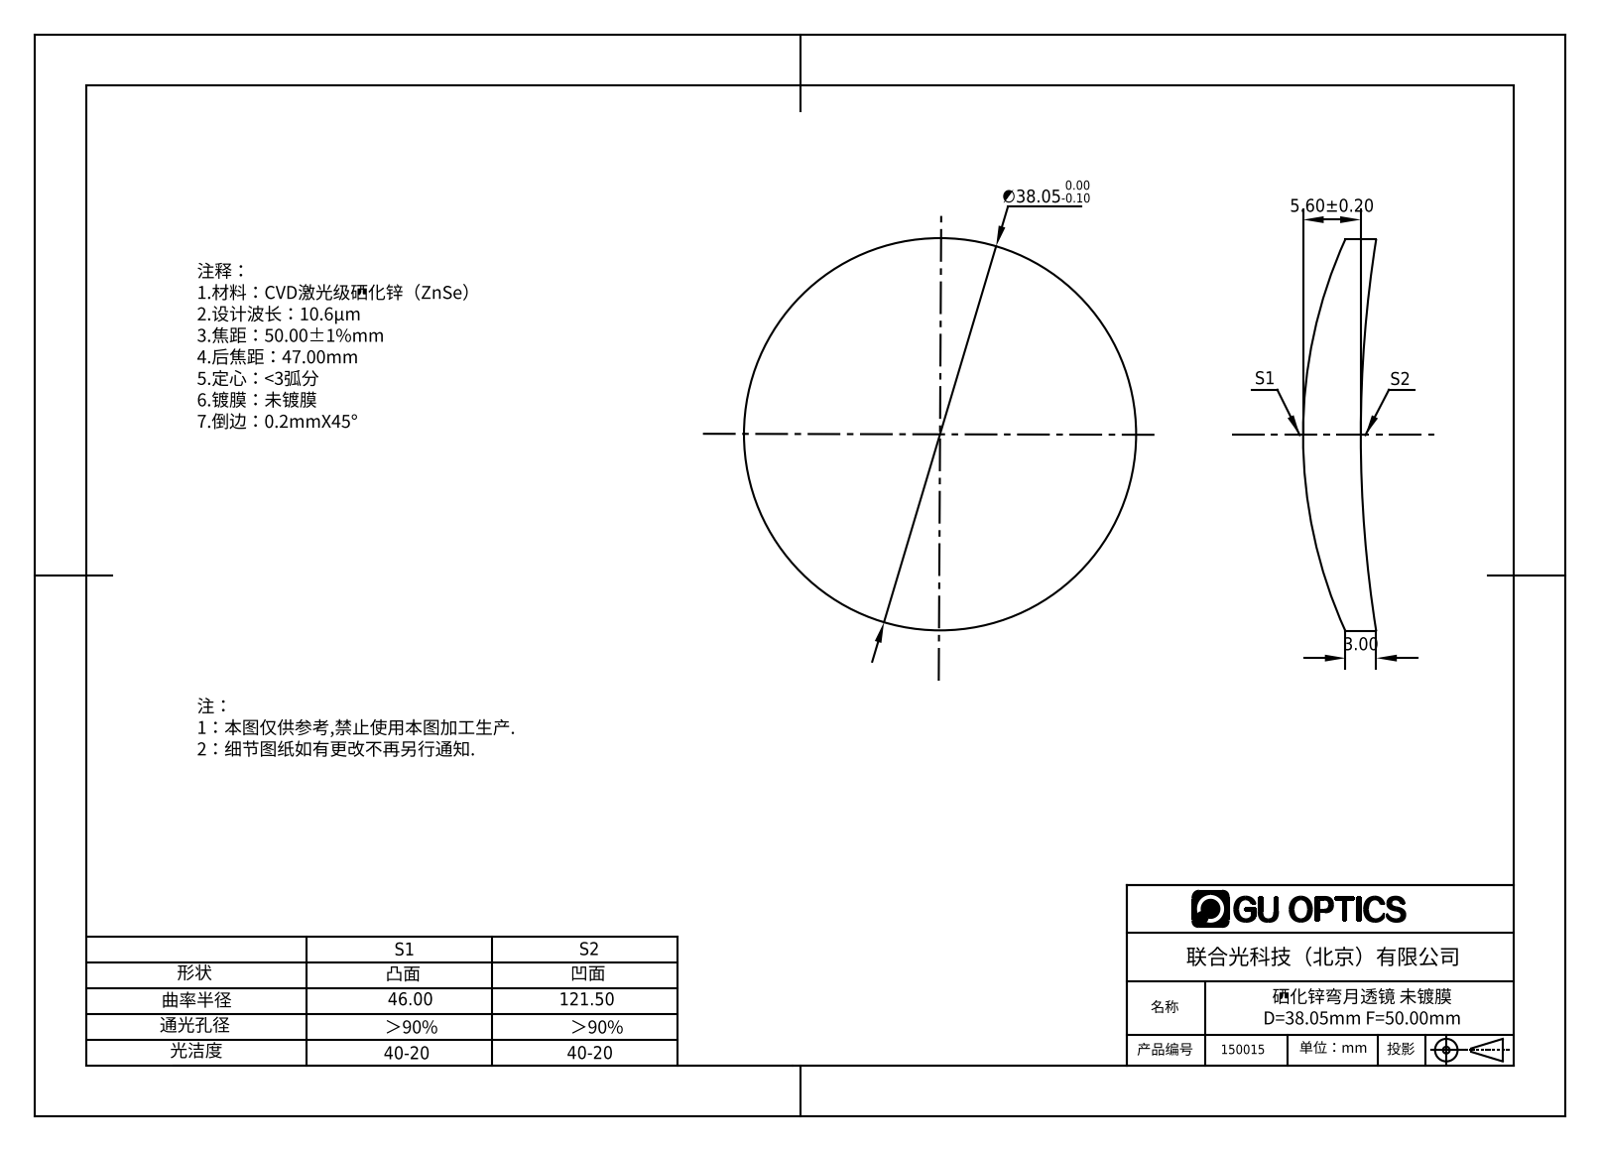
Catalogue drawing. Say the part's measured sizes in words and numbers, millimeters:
The part is named "150015". Its 3-D file was written by "SolidWorks 2016 (AUTOMOTIVE_DESIGN)". It is 1 solid with 6 faces: 0 planar, 2 cylindrical and 4 other. Overall it measures 38.05 by 38.05 by 7.1 millimeters. Its volume is 4 913 cubic millimeters and its surface area 2 691 square millimeters. Round bosses or shafts: 1 of diameter 38.05.
